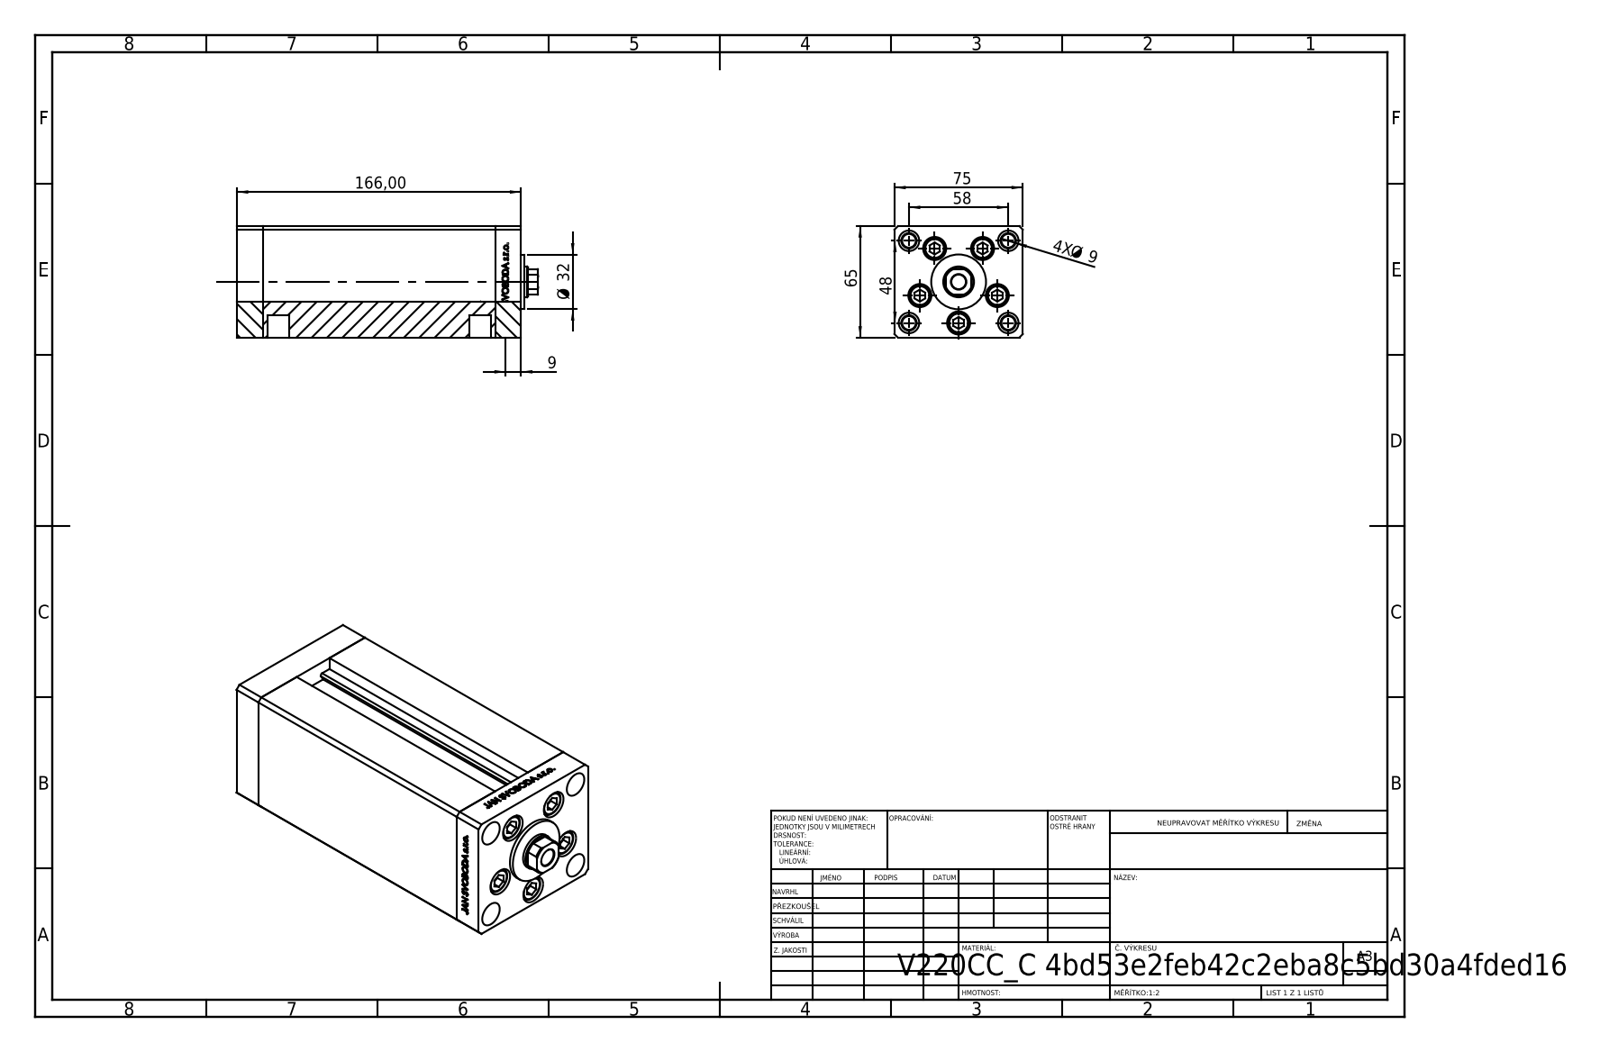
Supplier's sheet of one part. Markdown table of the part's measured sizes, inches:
| quantity | value |
| --- | --- |
| part name | V220C FRONT; ALLEN BOLT; V220C BACK_C; V220C_C MIDDLE (+1 more) |
| STEP written by | SolidWorks 2019 (CONFIG_CONTROL_DESIGN) |
| units | inches |
| bodies | 13 solids, 1179 faces (542 planar, 175 cylindrical, 462 other) |
| overall size | 6.929 × 2.953 × 2.559 |
| volume | 41.31 in³ |
| surface area | 222.8 in² |
| round holes (diameter × count) | 0.354 × 9, 0.531 × 5, 0.079 × 4, 0.315 × 4, 0.472 × 4, 0.518 × 4, 0.335 × 1, 0.492 × 1, 0.709 × 1 |
| round bosses / shafts (diameter × count) | 0.315 × 5, 0.492 × 4, 1.26 × 1 |
| partial cylindrical surfaces (radius × count) | 0.037 × 2, 0.335 × 1 |
| main face-to-face distances | 2.953, 2.559, 0.591, 5.354, 5.945, 6.535, 1.102, 0.512, 5.591, 0.354 |
| hole center spacings | 0.945, 1.482, 0.617, 0.678, 1.091, 1.135, 1.142, 1.285 |
